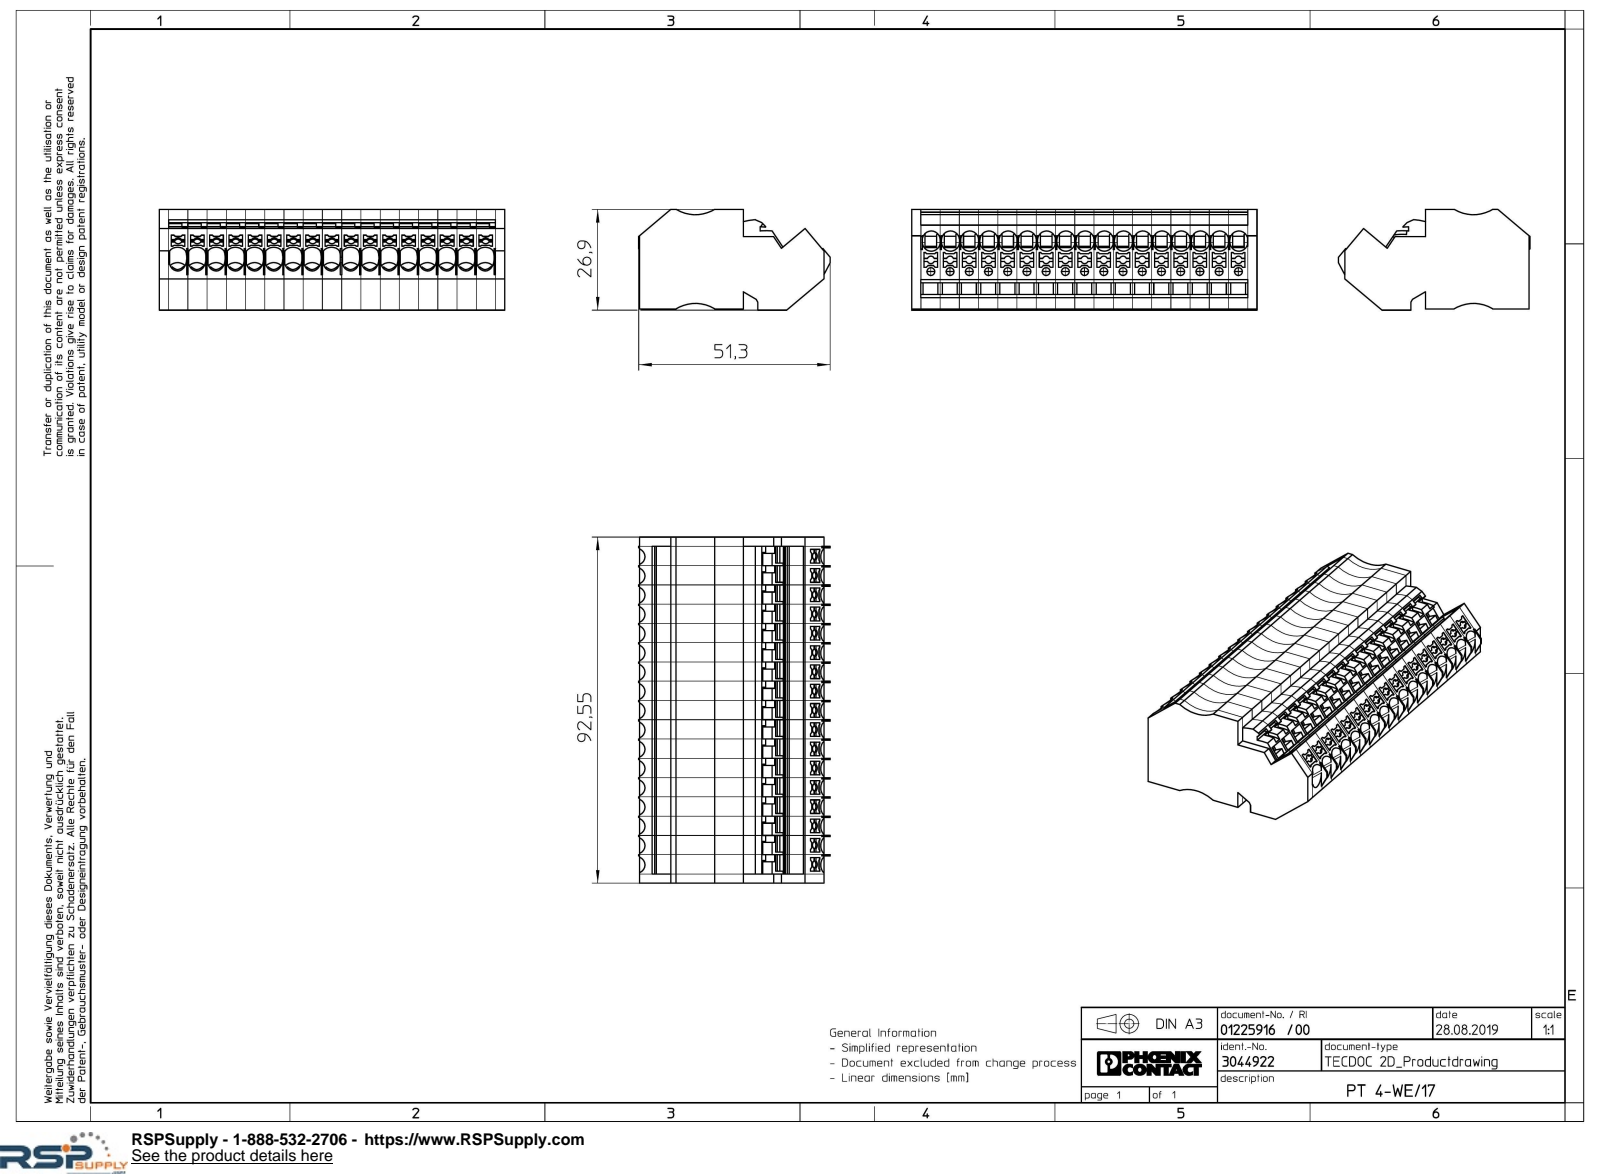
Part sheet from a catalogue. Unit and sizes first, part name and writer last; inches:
Units: inches
Overall size (bounding box): 3.644 × 2.02 × 1.059
Round holes (diameter × count): ⌀0.083 ×17
Partial cylindrical surfaces — rounded edges, fillets, slot ends (radius × count): R0.094 ×68, R0.039 ×34, R0.041 ×3, R0.394 ×2, R0.041 ×1, R0.07 ×1, R0.488 ×1, R0.527 ×1
Main face-to-face distances: 0.124, 0.152, 0.276, 3.644, 0.203, 0.406, 0.772, 0.608, 1.047, 0.896
Hole centre spacings: 0.203, 0.406, 0.608, 0.811, 1.014, 1.217, 1.419, 1.622
Volume: 5.08 in³ · Surface area: 49.62 in²
Bodies: 1 solid, 2839 faces (2461 planar, 344 cylindrical, 34 other)
Part name (STEP PRODUCT): PT_4_WE_17-select
STEP written by: Creo Elements/Direct Modeling 20.1A 29-Sep-2018 (C) Parametric Technology GmbH (AUTOMOTIVE_DESIGN)
